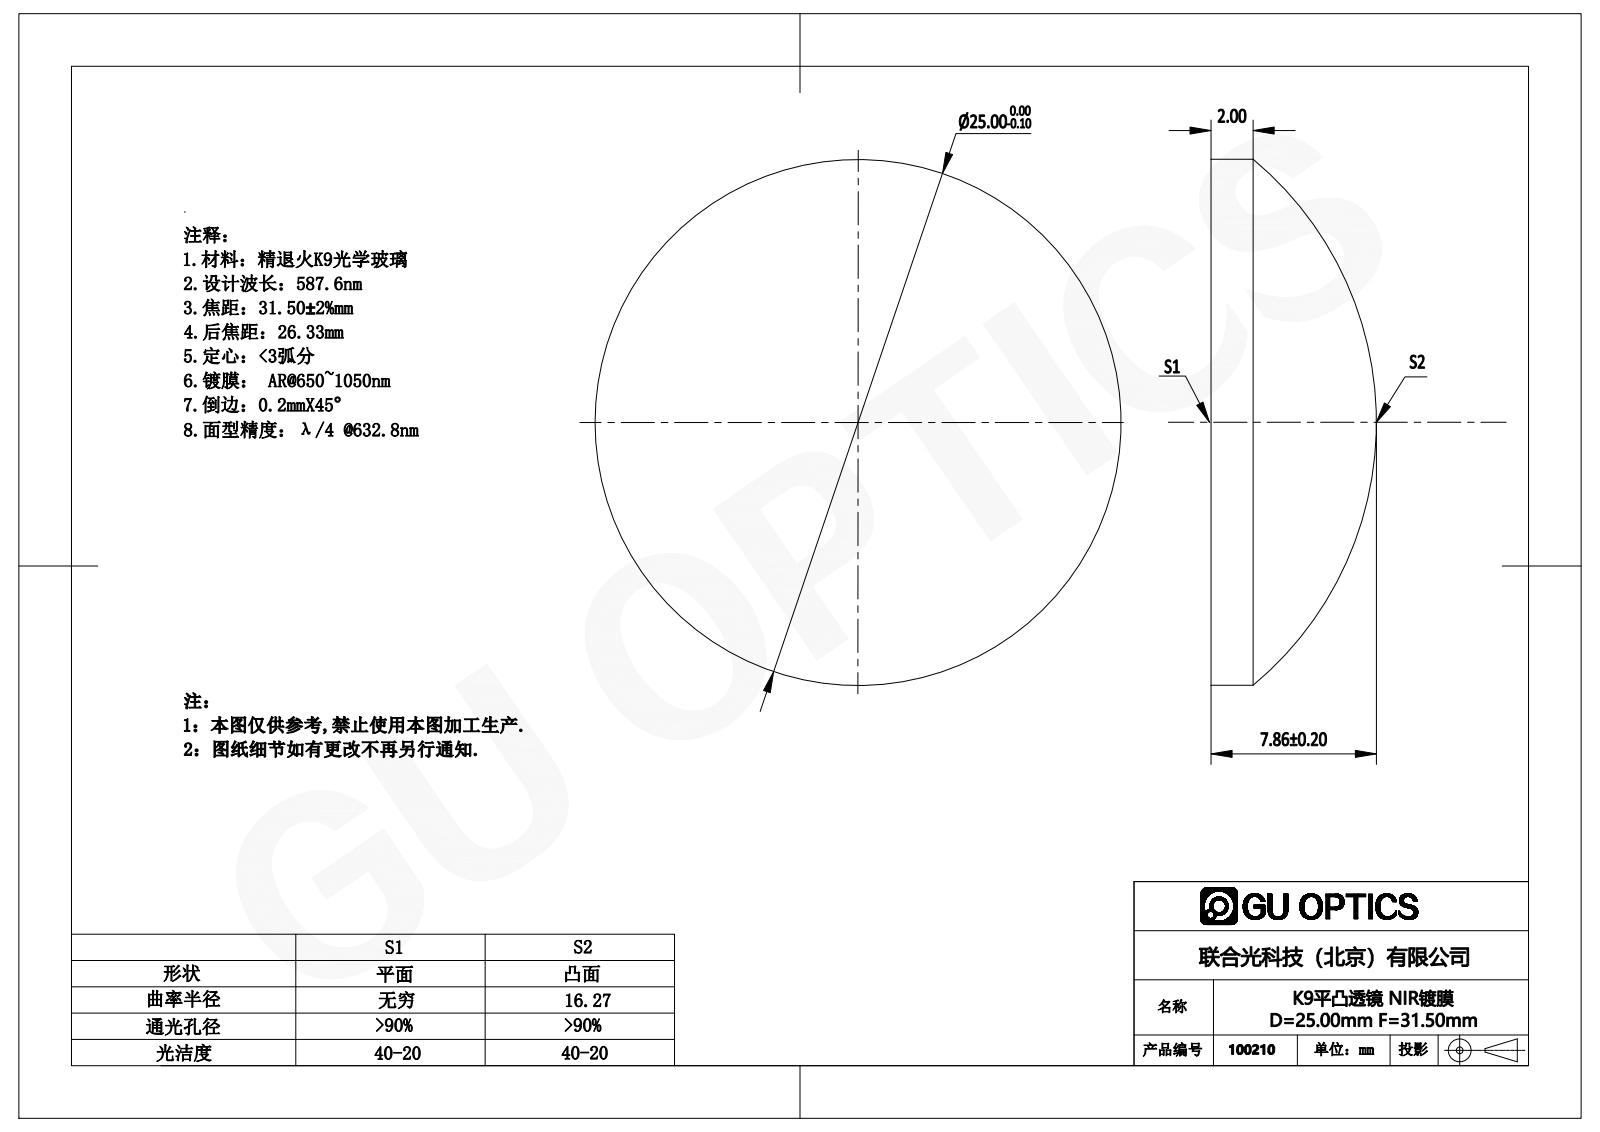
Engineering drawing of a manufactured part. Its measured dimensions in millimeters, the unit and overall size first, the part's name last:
Units: millimetres
Overall size (bounding box): 25 × 25 × 7.86
Round bosses / shafts (diameter × count): ⌀25 ×1
Volume: 2 525 mm³ · Surface area: 1 247 mm²
Bodies: 1 solid, 5 faces (1 planar, 2 cylindrical, 2 other)
Part name (STEP PRODUCT): 100210
STEP written by: SolidWorks 2016 (AUTOMOTIVE_DESIGN)
